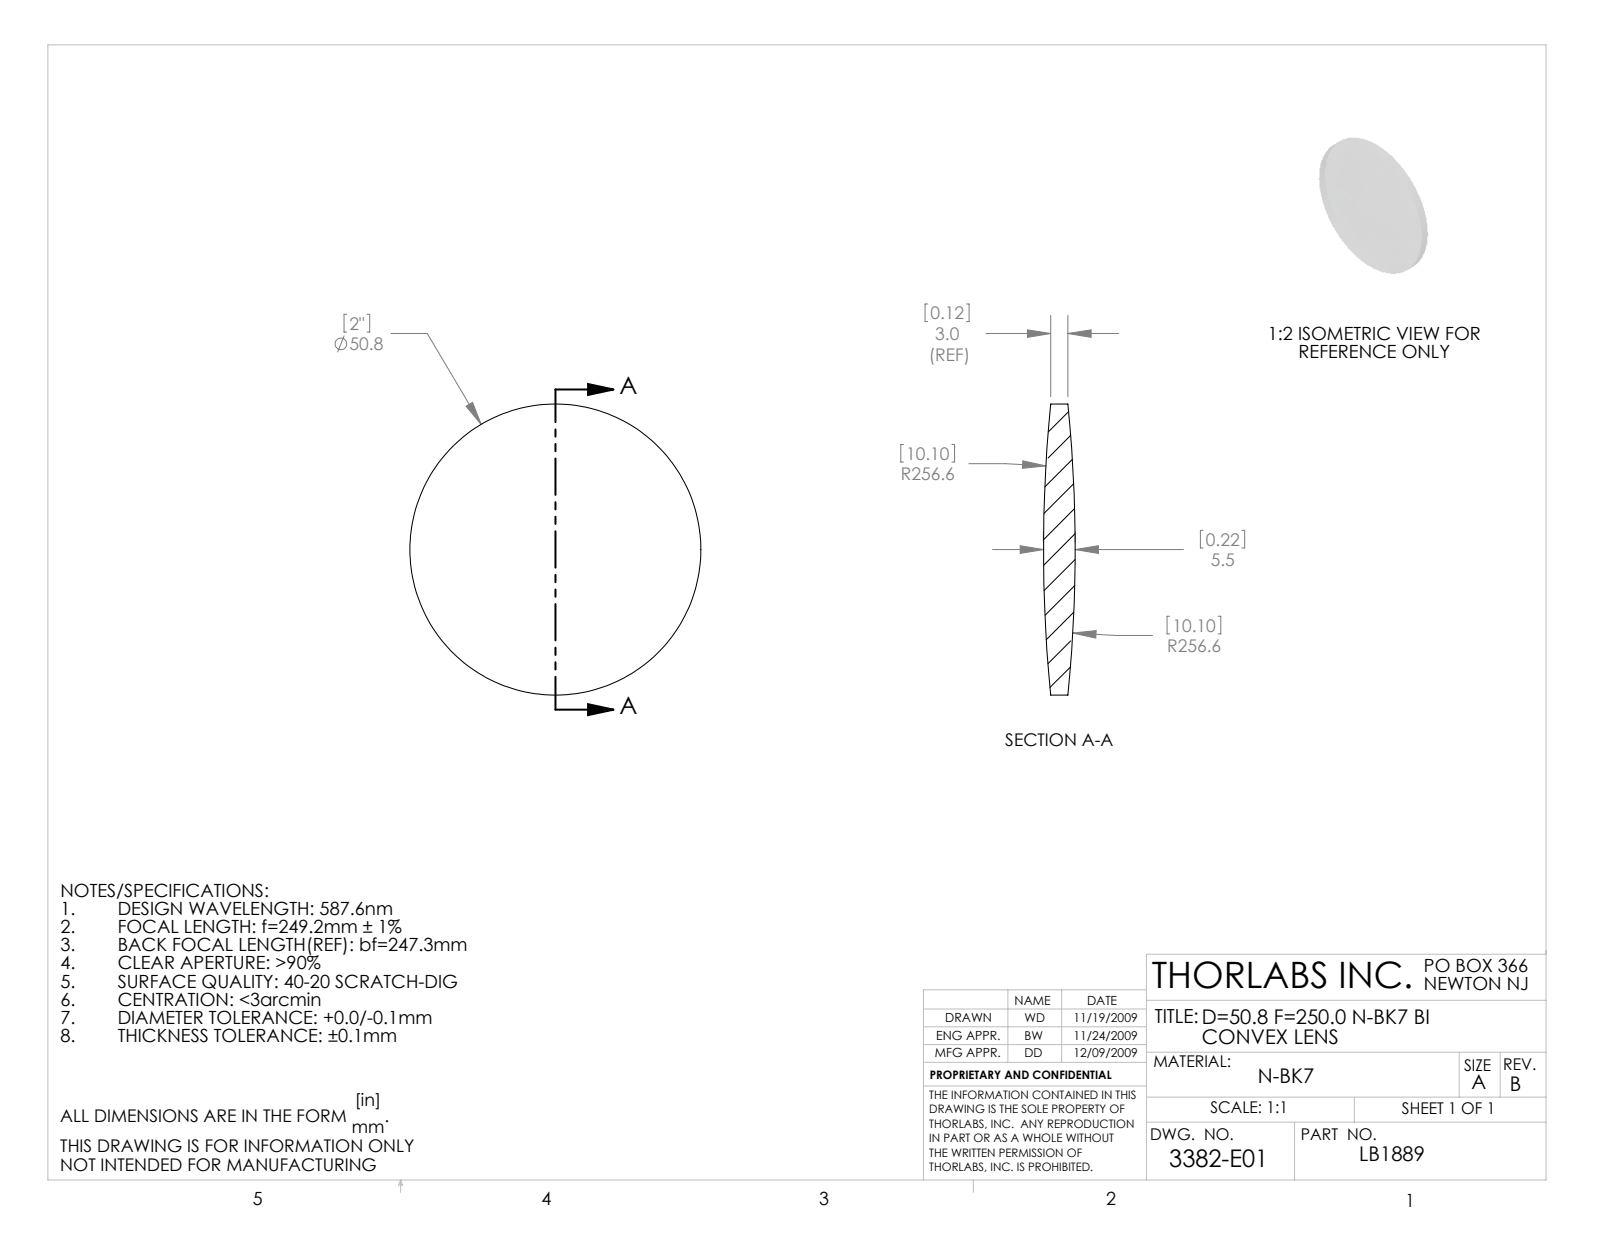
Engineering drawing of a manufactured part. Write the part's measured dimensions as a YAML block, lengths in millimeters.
part_name: "3382-E0W"
step_written_by: "SolidWorks 2009 (AUTOMOTIVE_DESIGN)"
units: millimeters
bodies: {solids: 1, faces: 6, planar: 0, cylindrical: 2, other: 4}
overall_size: [50.8, 50.8, 5.52]
volume: 8636
surface_area: 4542
round_bosses_or_shafts:
  - {diameter: 50.8, count: 1}
